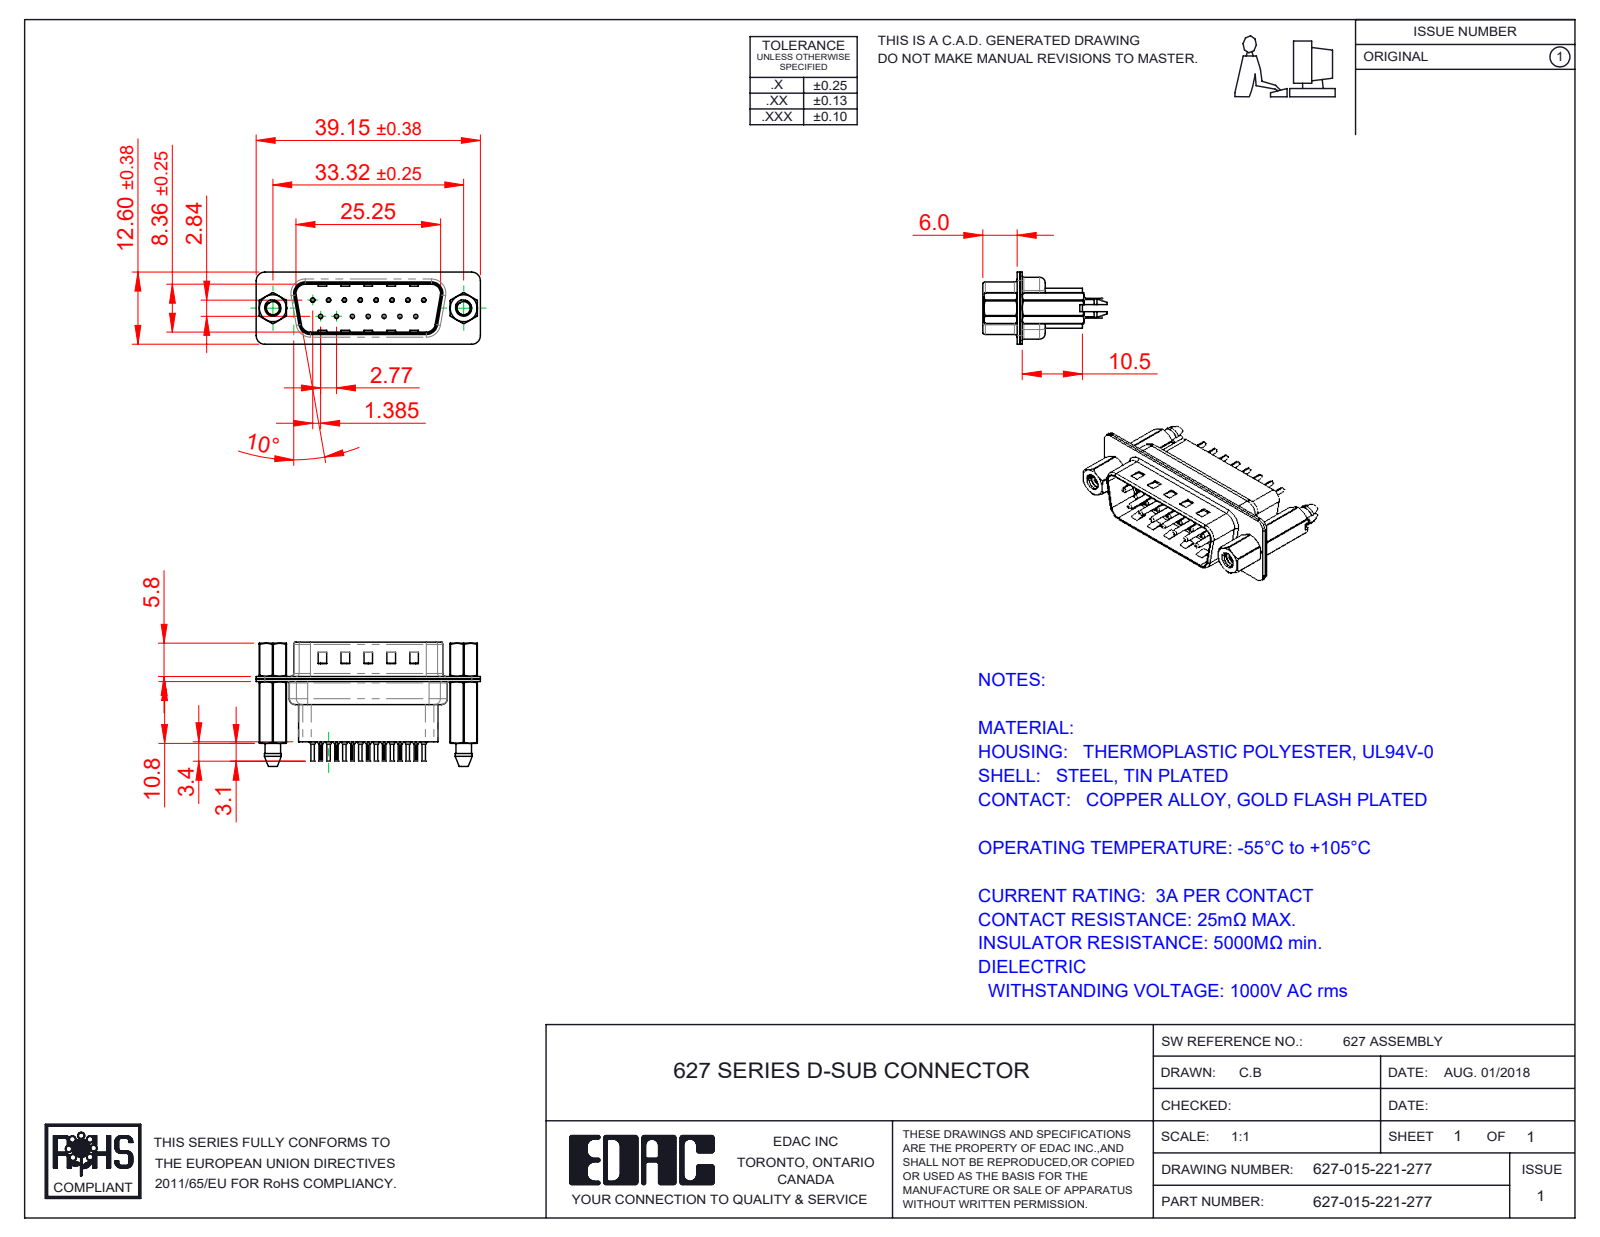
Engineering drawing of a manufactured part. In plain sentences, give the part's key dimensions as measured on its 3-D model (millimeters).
The part is named "627 Contact Row 1_21H; 627 4-40 Threaded Boardlock_HP; 627 4-40 Hex Standoff; 627 Shell Rear_15 Contacts (+4 more)". Its 3-D file was written by "SolidWorks 2020 (CONFIG_CONTROL_DESIGN)". It is 22 solids with 2050 faces: 553 planar, 828 cylindrical and 669 other. Overall it measures 39.15 by 21.7 by 12.6 millimeters. Its volume is 3 002 cubic millimeters and its surface area 7 676 square millimeters. Round holes: 15 of diameter 0.2, 15 of diameter 0.35, 15 of diameter 1.1, 15 of diameter 1.6, 2 of diameter 2.26, 2 of diameter 2.29, 2 of diameter 4, 2 of diameter 4.8. Round bosses or shafts: 15 of diameter 2, 15 of diameter 1.5, 15 of diameter 0.75, 15 of diameter 0.6, 2 of diameter 4.9, 2 of diameter 2.79. Partial cylindrical surfaces (rounded edges, fillets, slot ends): 30 of radius 0.1, 18 of radius 1.5, 12 of radius 2, 10 of radius 1.6, 8 of radius 0.5, 4 of radius 0.25, 4 of radius 0.6, 4 of radius 0.65. The main face-to-face distances are 0.4, 0.45, 0.9, 0.82, 9.58, 4.76, 1.5, 0.68, 7.68, 1.4. The hole center spacings are 3.16, 2.77, 5.54, 8.31, 11.08, 5.03, 5.04, 7.48.
